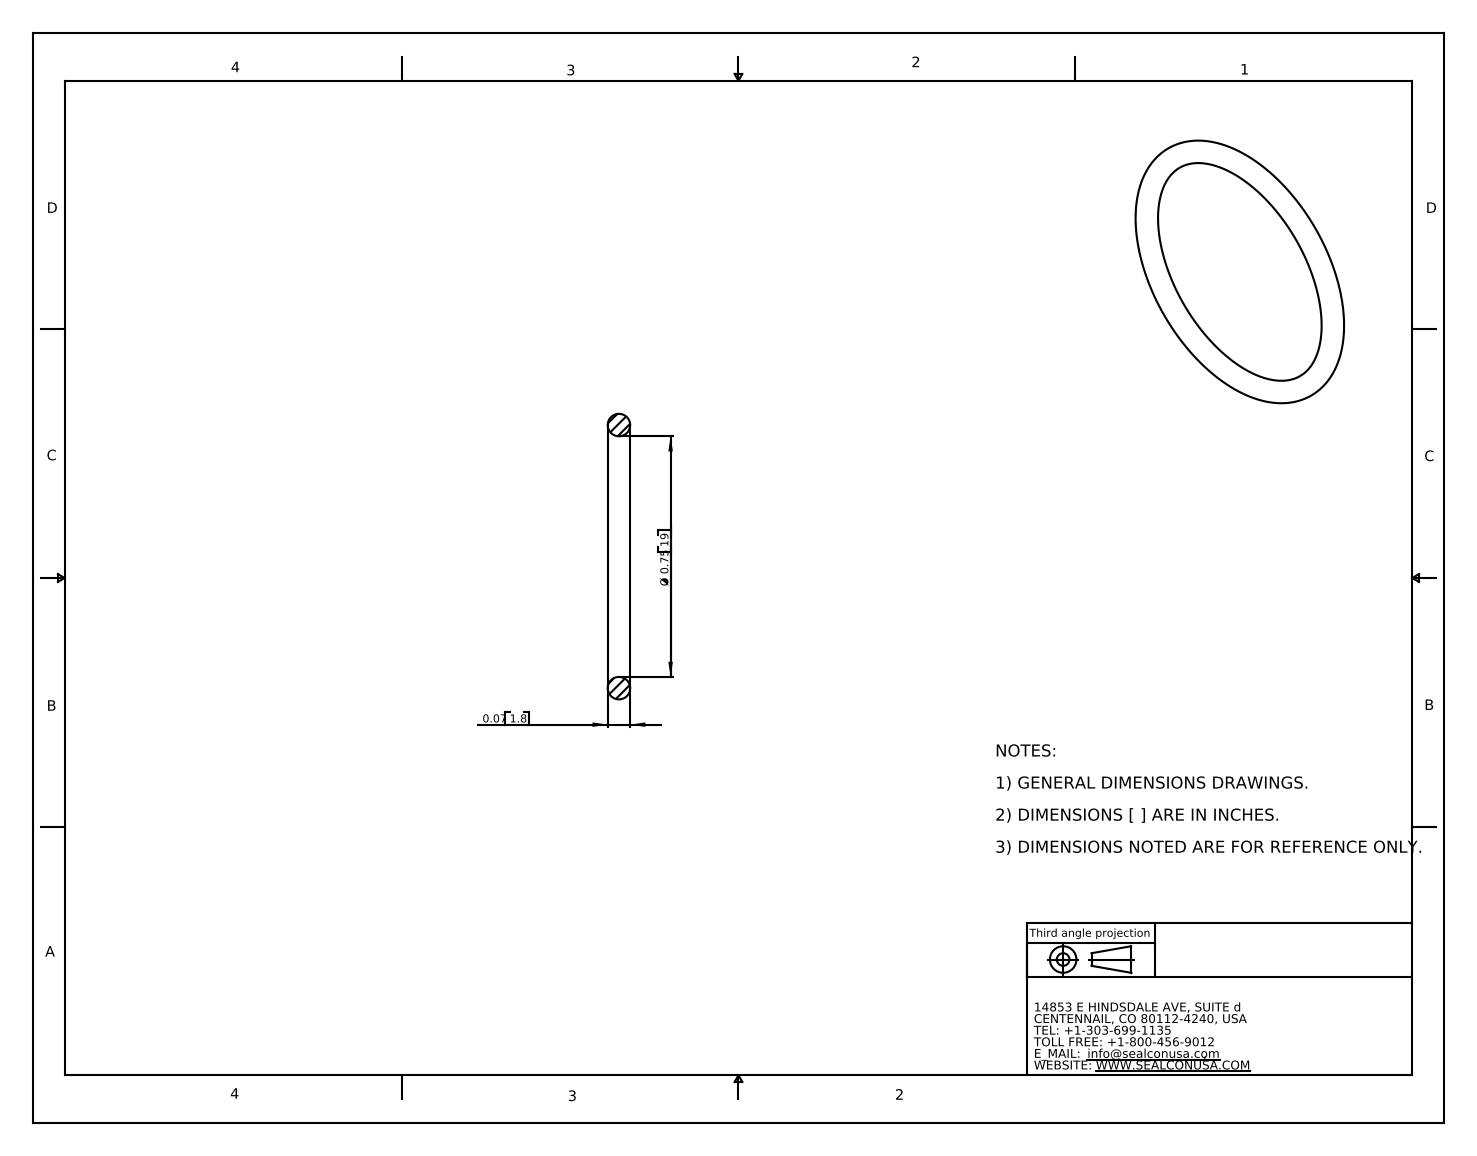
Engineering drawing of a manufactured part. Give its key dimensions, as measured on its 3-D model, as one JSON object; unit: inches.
{"part_name": "OR-18-VT", "step_written_by": "SolidWorks 2007 (CONFIG_CONTROL_DESIGN)", "units": "inches", "bodies": {"solids": 1, "faces": 4, "planar": 0, "cylindrical": 0, "other": 4}, "overall_size": [0.89, 0.89, 0.07], "volume_in3": 0.01, "surface_area_in2": 0.567}
